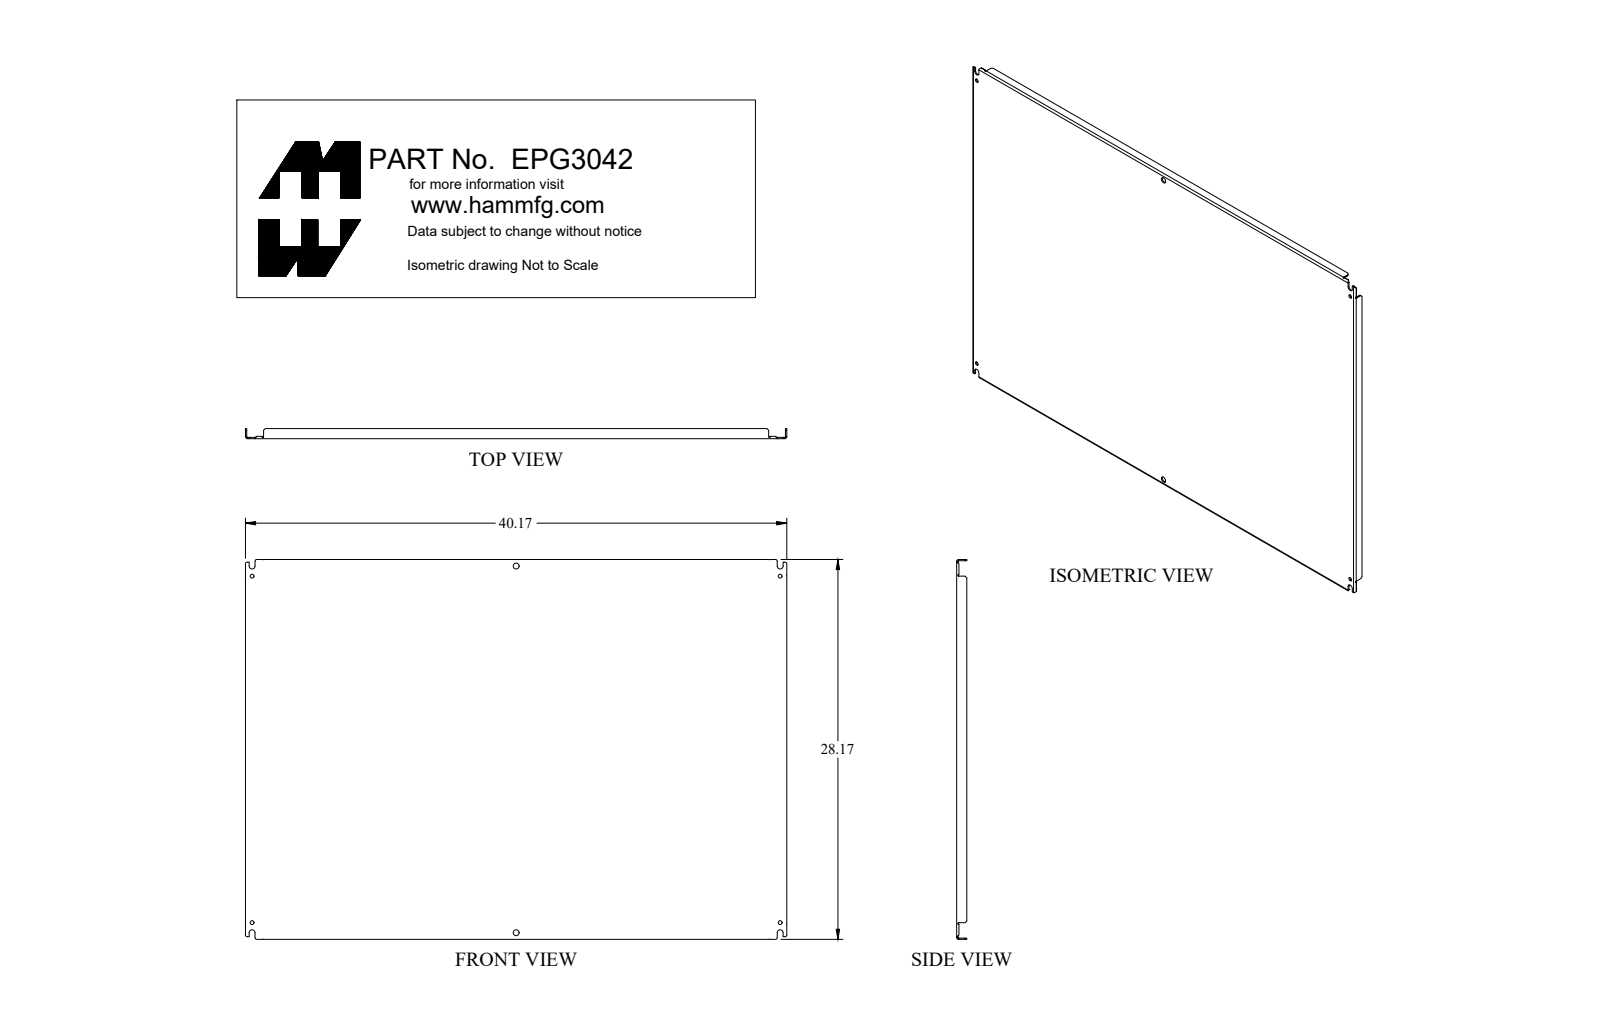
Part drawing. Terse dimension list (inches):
name: EPG3042
written by: SolidWorks 2018 (AUTOMOTIVE_DESIGN)
unit: in
bodies: 1 solid, 132 faces (74 planar, 42 cylindrical, 16 other)
size: 40.17 × 28.17 × 0.75
volume: 114.7 in³; area: 2 429 in²
holes: 4× ⌀0.281, 2× ⌀0.437
rounds: 4× R0.048, 4× R0.063, 4× R0.143, 4× R0.219
face distances: 0.095, 28.075, 40.075, 28.17, 27.98, 39.98, 40.17, 0.75, 0.655, 0.171
hole spacings: 19.608, 32.907, 25.688, 39.188, 46.857, 27.188
